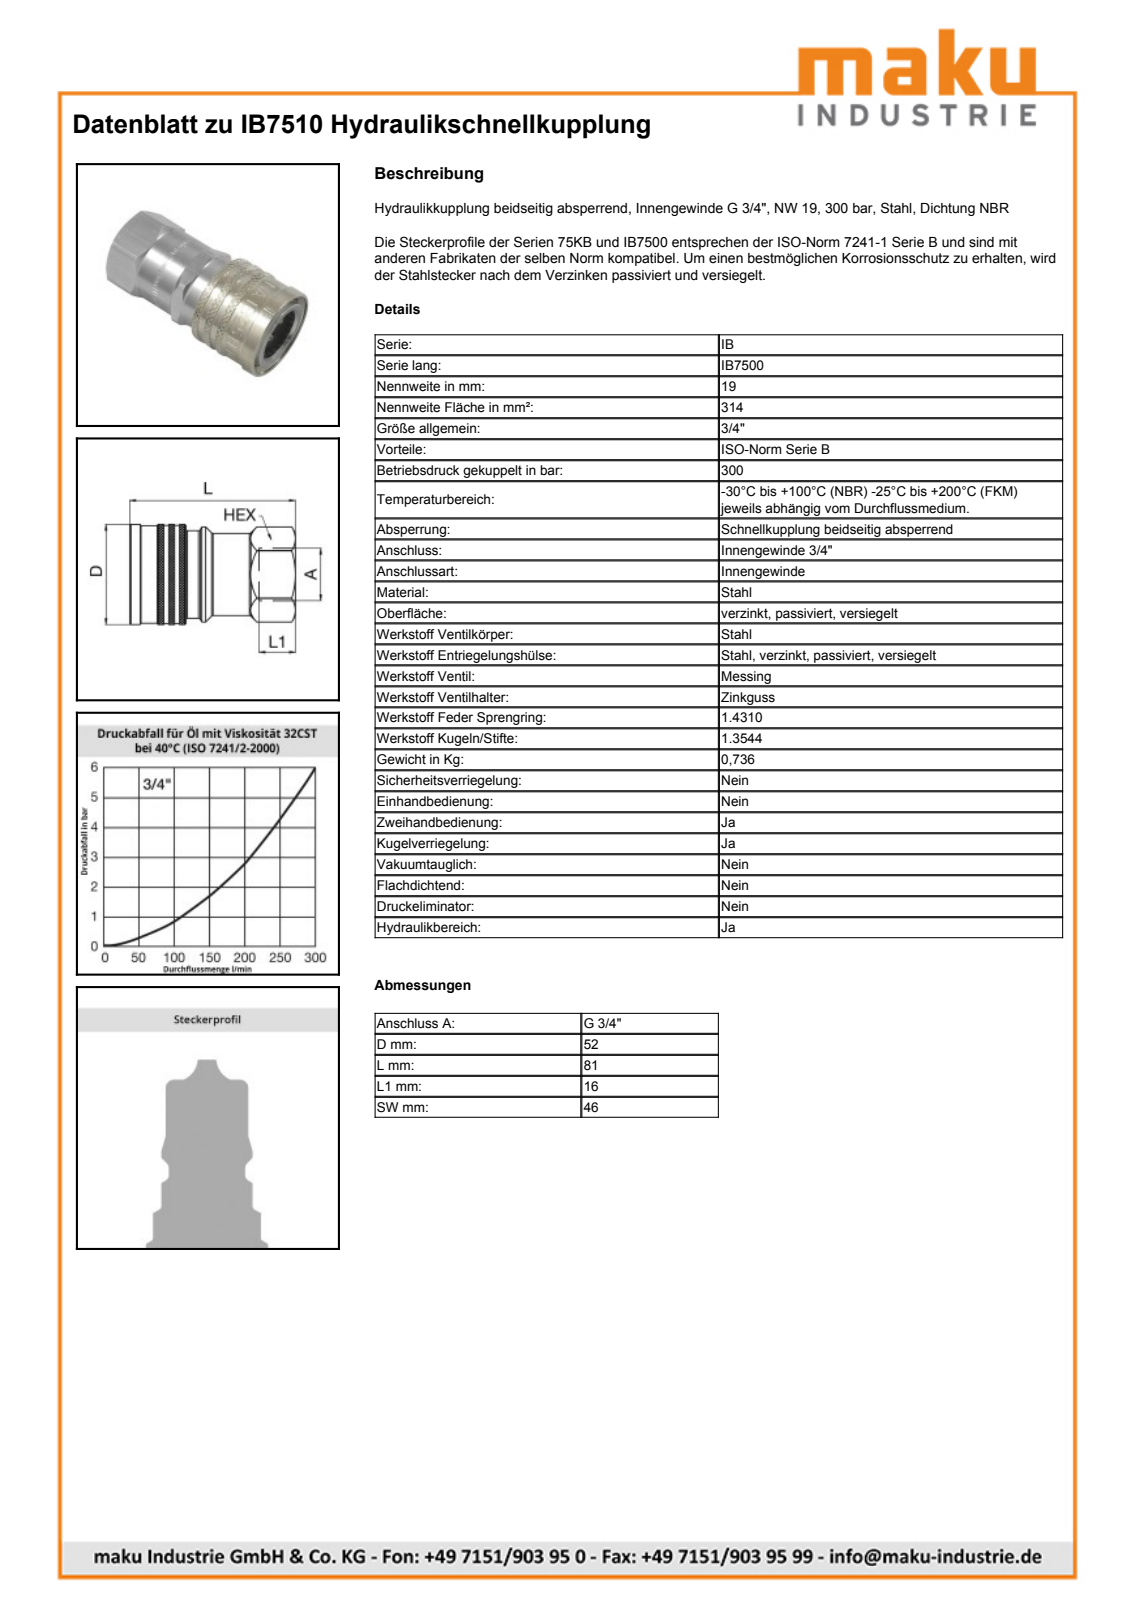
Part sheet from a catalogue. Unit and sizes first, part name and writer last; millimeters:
Units: millimetres
Overall size (bounding box): 81 × 52 × 52
Round holes (diameter × count): ⌀19 ×1, ⌀24.12 ×1, ⌀31.5 ×1, ⌀32.5 ×1, ⌀32.8 ×1, ⌀34.68 ×1, ⌀41.7 ×1, ⌀45.7 ×1, ⌀46.2 ×1
Round bosses / shafts (diameter × count): ⌀52 ×1, ⌀51.2 ×1, ⌀51 ×1, ⌀46 ×1, ⌀45.6 ×1, ⌀41.5 ×1, ⌀39.5 ×1
Partial cylindrical surfaces — rounded edges, fillets, slot ends (radius × count): R25 ×1
Main face-to-face distances: 46, 14.35, 47, 32.65, 5.35, 81, 66.65, 34, 52.35, 38
Volume: 114 095 mm³ · Surface area: 26 384 mm²
Bodies: 2 solids, 302 faces (31 planar, 79 cylindrical, 192 other)
Part name (STEP PRODUCT): IB7510
STEP written by: SolidWorks 2009 (AUTOMOTIVE_DESIGN)
